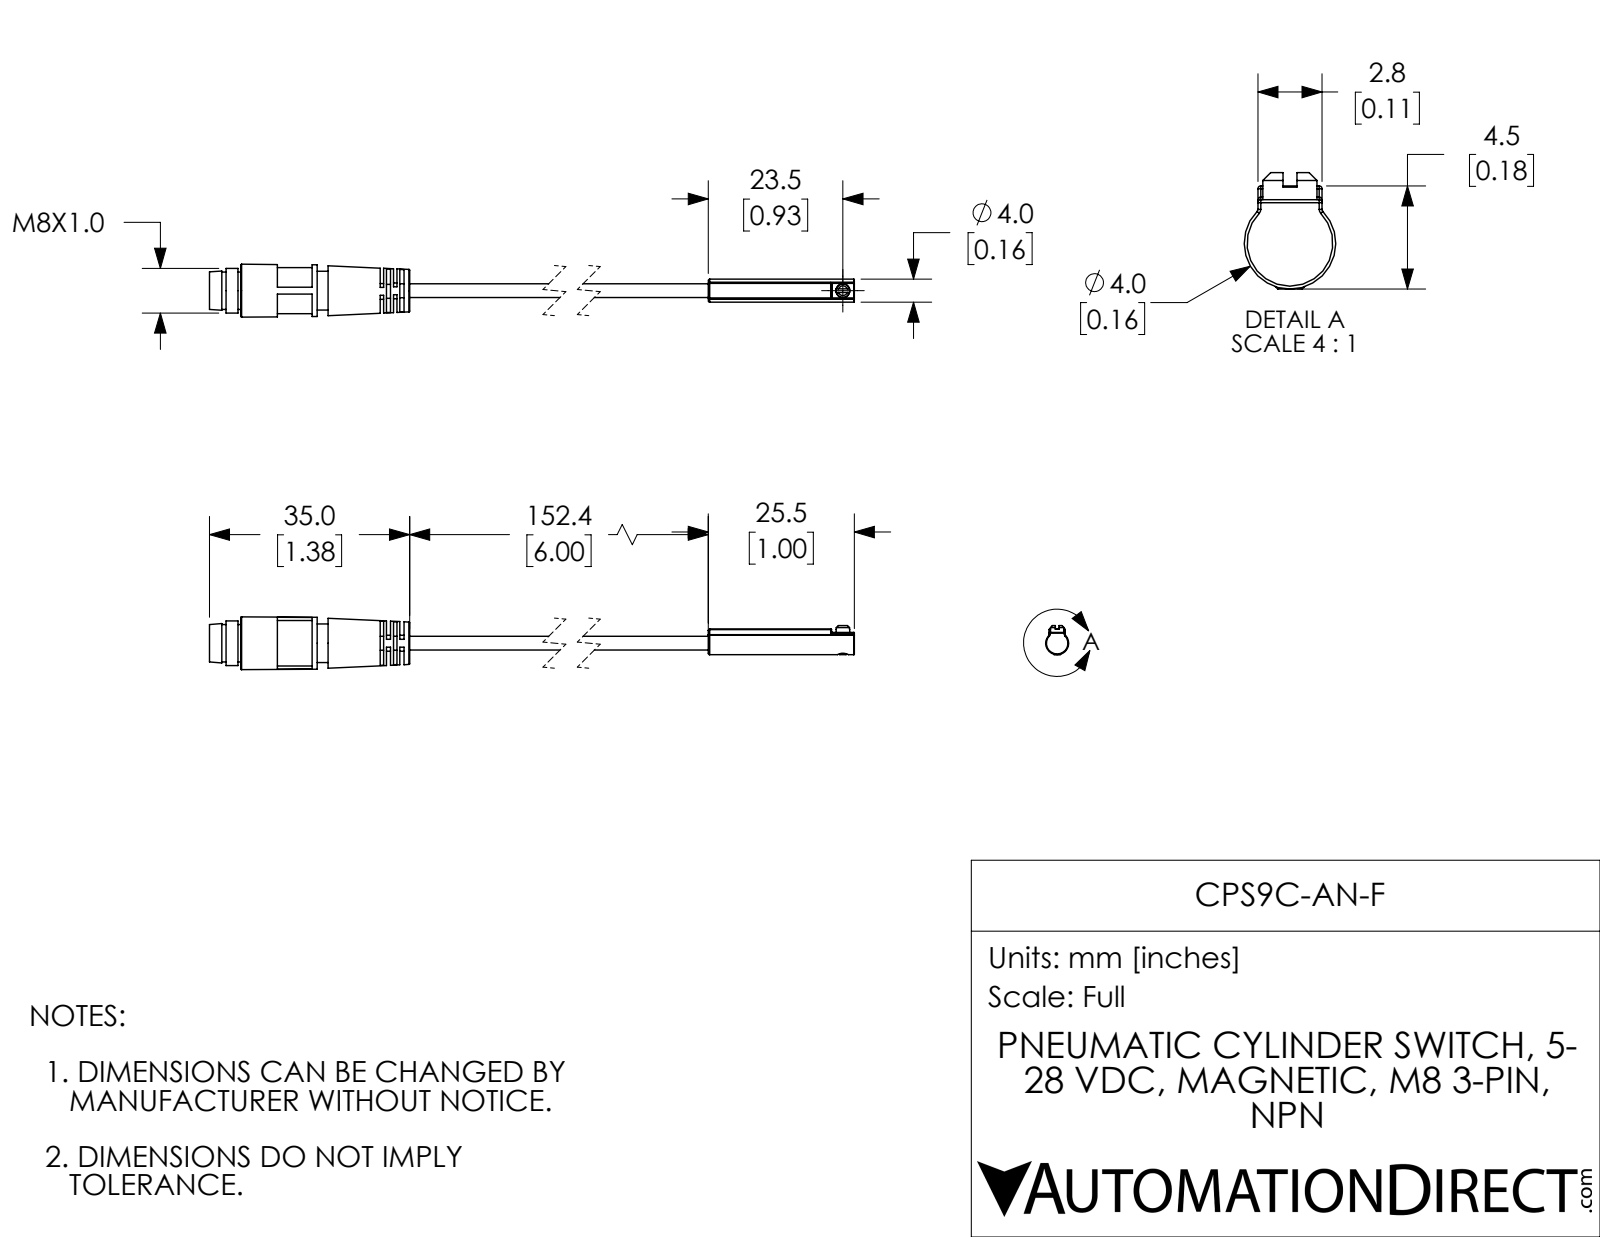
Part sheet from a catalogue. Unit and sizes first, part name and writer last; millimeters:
Units: millimetres
Overall size (bounding box): 212.9 × 9.2 × 9.2
Round holes (diameter × count): ⌀1.9 ×1, ⌀5.4 ×1, ⌀5.8 ×1
Round bosses / shafts (diameter × count): ⌀1 ×3, ⌀8 ×1, ⌀7.8 ×1, ⌀6.8 ×1, ⌀6.5 ×1, ⌀2.4 ×1, ⌀2.4 ×1
Partial cylindrical surfaces — rounded edges, fillets, slot ends (radius × count): R0.1 ×13, R0.3 ×3, R1.4 ×2, R1.4 ×2, R2 ×1
Main face-to-face distances: 1.2, 1.8, 2.3, 0.6, 0.5, 1.1, 27.3, 24.9, 0.5, 27.8
Volume: 2 650 mm³ · Surface area: 3 092 mm²
Bodies: 3 solids, 167 faces (67 planar, 55 cylindrical, 45 other)
Part name (STEP PRODUCT): CPS9C-AN-F
STEP written by: SolidWorks 2019 (AUTOMOTIVE_DESIGN)
